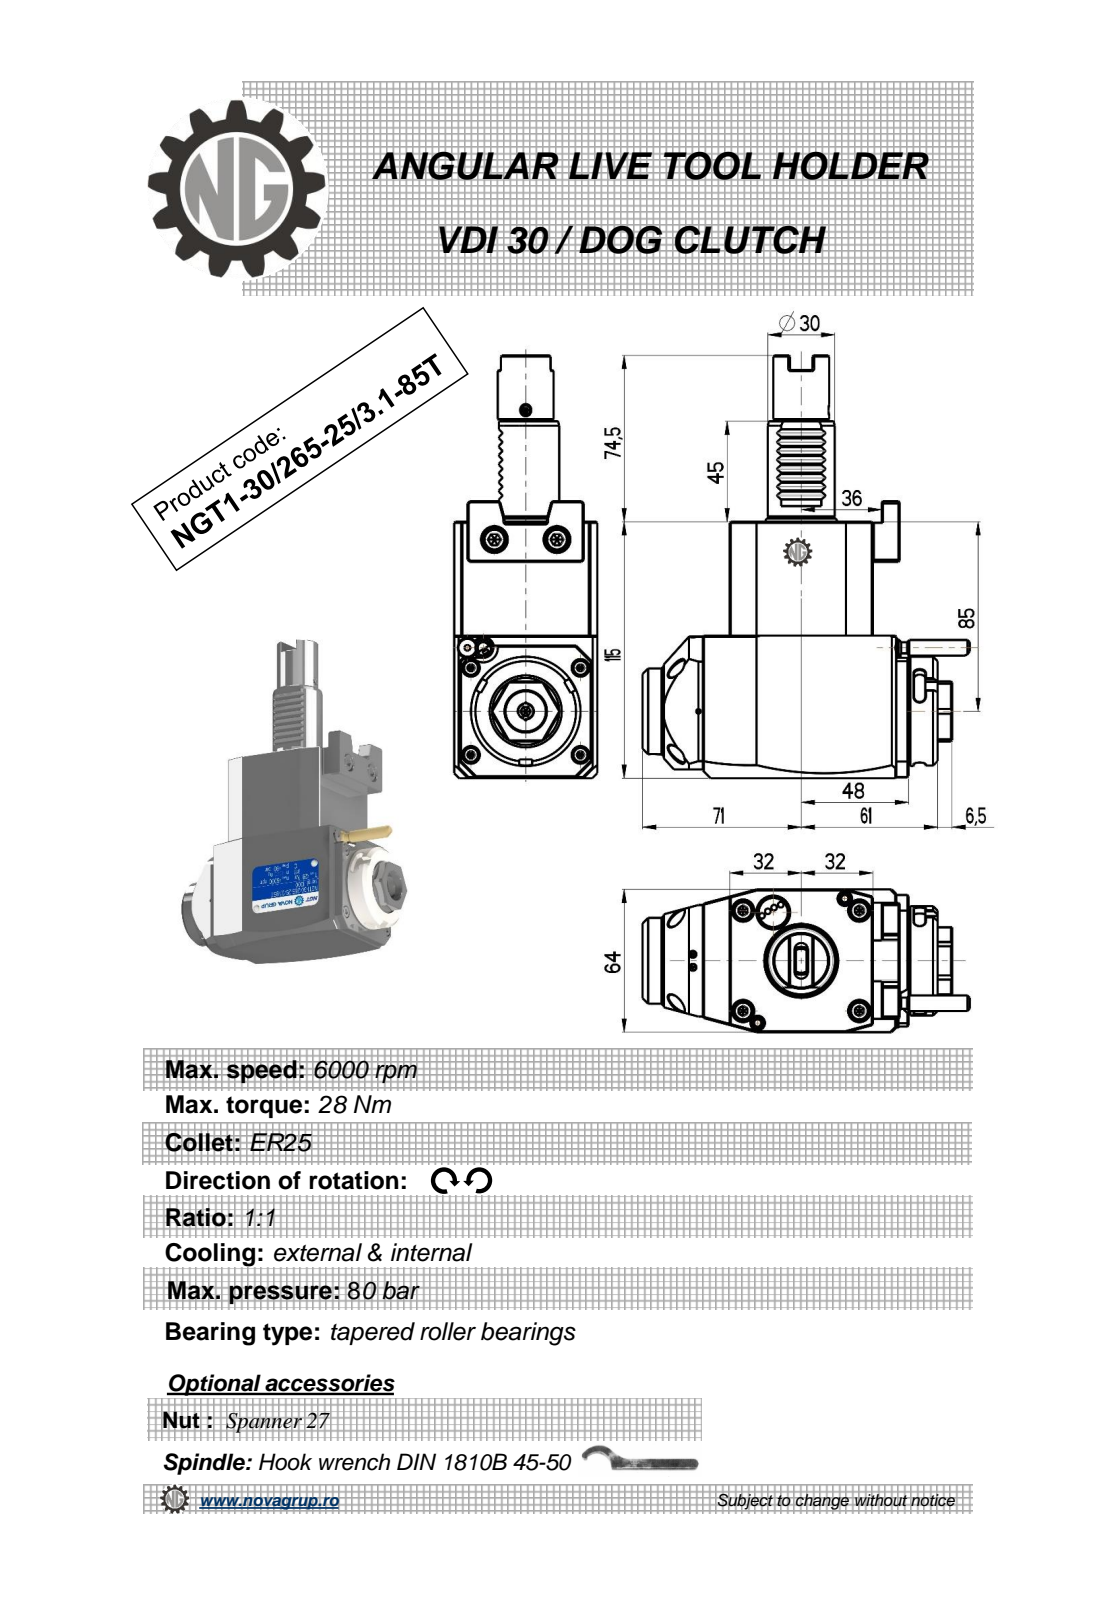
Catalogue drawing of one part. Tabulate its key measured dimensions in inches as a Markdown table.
| quantity | value |
| --- | --- |
| part name | NGT1_30_265_25_3_1_85T |
| STEP written by | PRO/ENGINEER BY PARAMETRIC TECHNOLOGY CORPORATION, 2010280 (CONFIG_CONTROL_DESIGN) |
| units | inches |
| bodies | 1 solid, 327 faces (202 planar, 65 cylindrical, 60 other) |
| overall size | 7.461 × 5.763 × 2.52 |
| volume | 42.66 in³ |
| surface area | 93.03 in² |
| round holes (diameter × count) | 0.098 × 1, 0.118 × 1, 0.165 × 1, 0.709 × 1 |
| round bosses / shafts (diameter × count) | 1.929 × 1, 1.654 × 1, 1.516 × 1, 1.181 × 1, 0.984 × 1, 0.821 × 1, 0.315 × 1, 0.276 × 1 |
| partial cylindrical surfaces (radius × count) | 0.012 × 8, 0.01 × 6, 0.098 × 6, 0.02 × 2, 0.039 × 2, 7.087 × 2, 0.177 × 1, 0.591 × 1 |
| main face-to-face distances | 2.52, 4.528, 3.15, 0.63, 0.157, 0.472, 3.661, 2.008, 2.992, 0.512 |
| hole center spacings | 1.348, 4.259, 5.315 |
